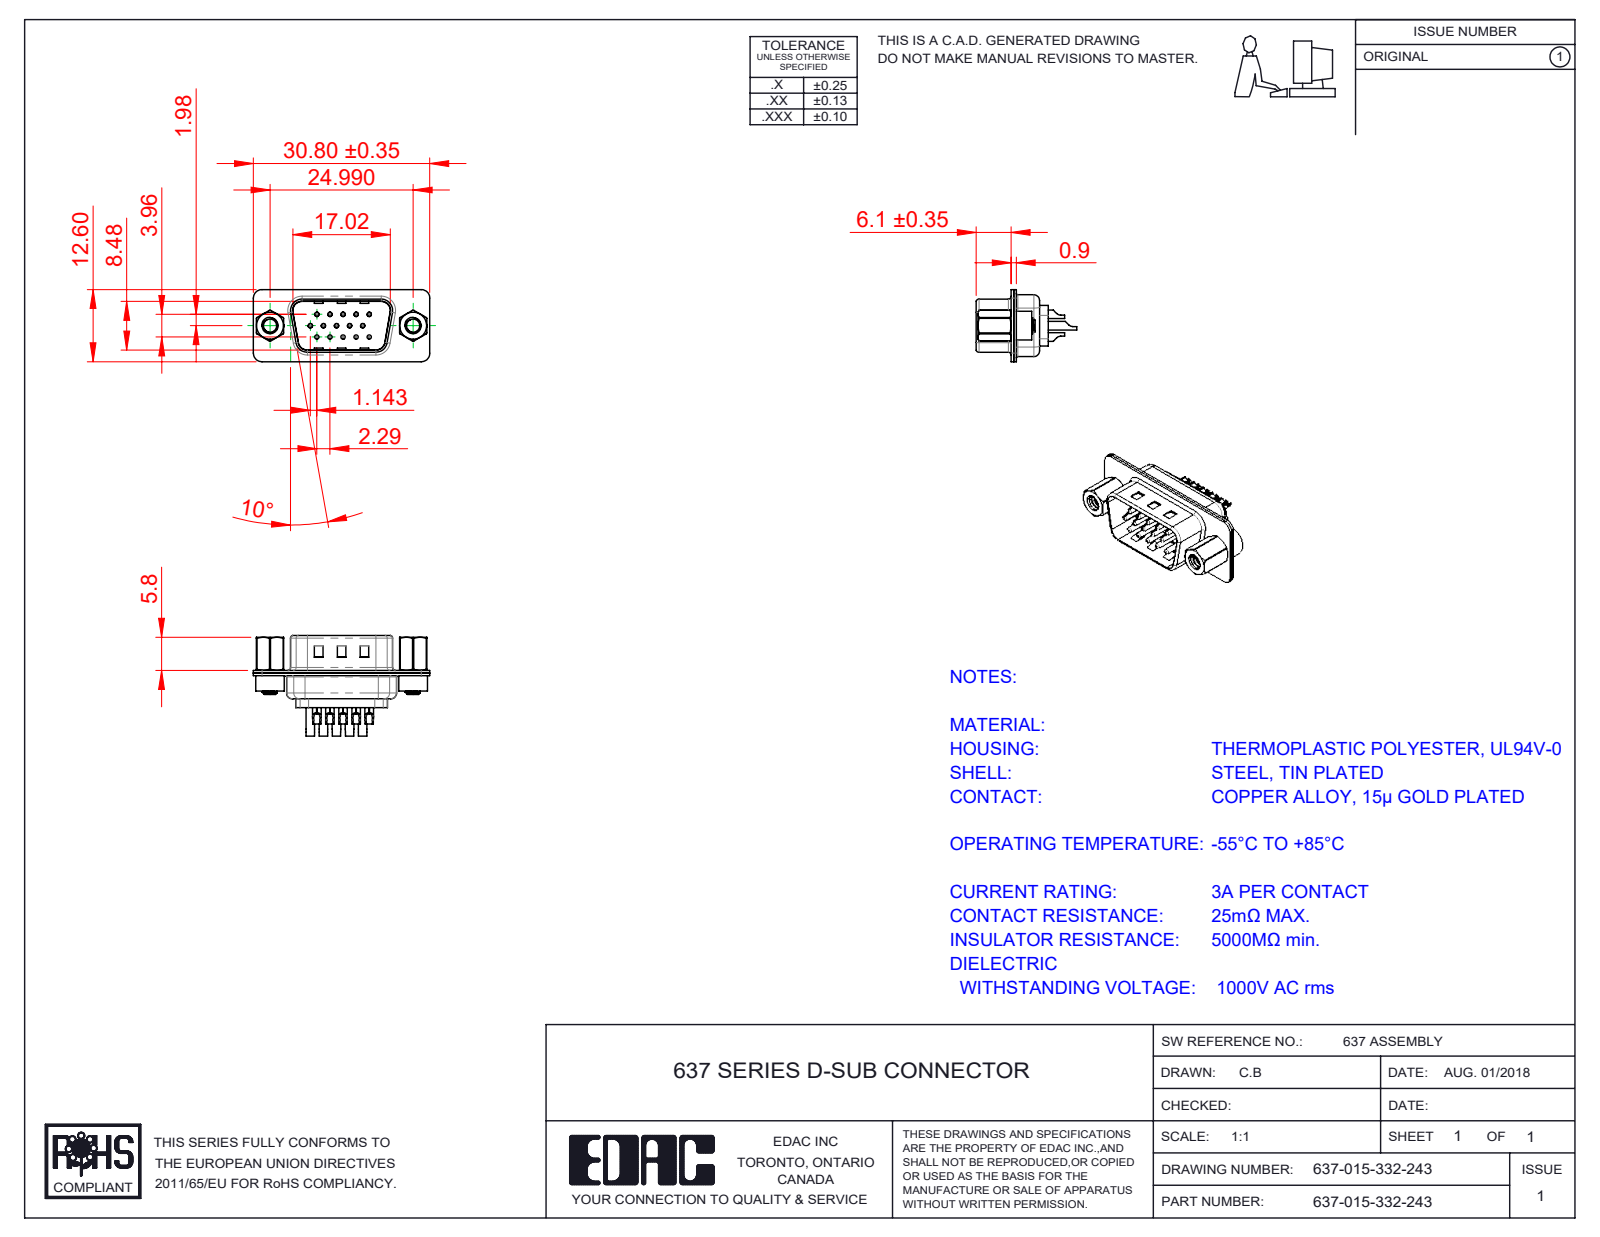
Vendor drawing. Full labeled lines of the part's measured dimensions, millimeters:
Part name (STEP PRODUCT): 637 Housing_15 Contacts; 637-015-332-243; 637 Contact Row 3_32; 637 Contact Row 1_32 (+5 more)
STEP written by: SolidWorks 2020 (CONFIG_CONTROL_DESIGN)
Units: millimetres
Bodies: 22 solids, 1390 faces (339 planar, 636 cylindrical, 415 other)
Overall size (bounding box): 30.8 × 17.55 × 12.6
Volume: 1 544 mm³ · Surface area: 5 262 mm²
Round holes (diameter × count): ⌀0.35 ×15, ⌀1.1 ×15, ⌀1.6 ×15, ⌀2.26 ×2, ⌀2.29 ×2, ⌀4 ×2, ⌀4.8 ×2
Round bosses / shafts (diameter × count): ⌀2 ×15, ⌀1.5 ×15, ⌀0.75 ×15, ⌀5 ×2, ⌀4.9 ×2, ⌀2.79 ×2
Partial cylindrical surfaces — rounded edges, fillets, slot ends (radius × count): R1.5 ×16, R2 ×12, R0.5 ×8, R1 ×7, R0.25 ×4, R0.55 ×4, R0.7 ×4, R0.95 ×4
Main face-to-face distances: 0.45, 0.9, 0.4, 0.7, 8.88, 8.48, 1.05, 0.31, 4.55, 6.5
Hole centre spacings: 3.96, 2.28, 4.57, 2.29, 6.05, 6.86, 7.92, 6.04
